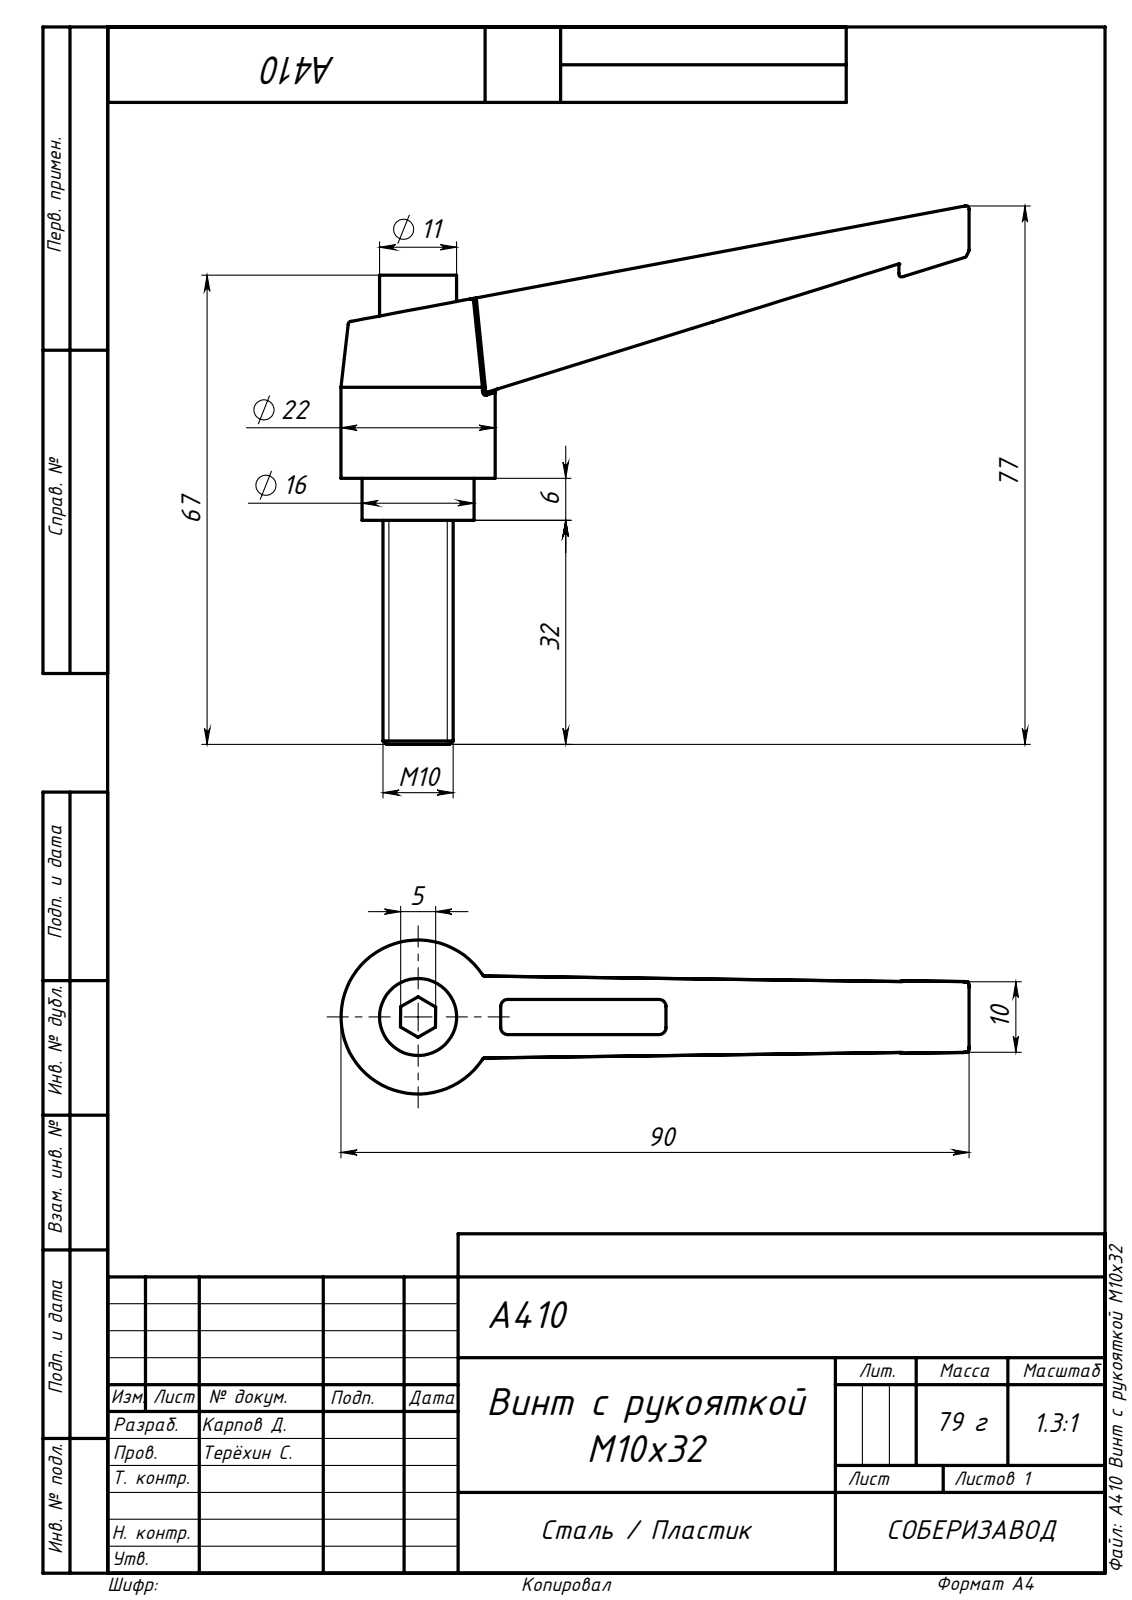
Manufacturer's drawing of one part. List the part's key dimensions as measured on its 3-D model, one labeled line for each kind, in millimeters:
Part name (STEP PRODUCT): A410 Винт с рукояткой М10х32
STEP written by: SolidWorks 2020 (AUTOMOTIVE_DESIGN)
Units: millimetres
Bodies: 1 solid, 81 faces (31 planar, 12 cylindrical, 38 other)
Overall size (bounding box): 89.62 × 76.91 × 22
Volume: 16 827 mm³ · Surface area: 7 271 mm²
Round bosses / shafts (diameter × count): ⌀22 ×1, ⌀16 ×1, ⌀11 ×1, ⌀10 ×1
Partial cylindrical surfaces — rounded edges, fillets, slot ends (radius × count): R1 ×4
Main face-to-face distances: 6, 32, 6.93, 35, 29, 38, 67, 60.48, 5, 64
